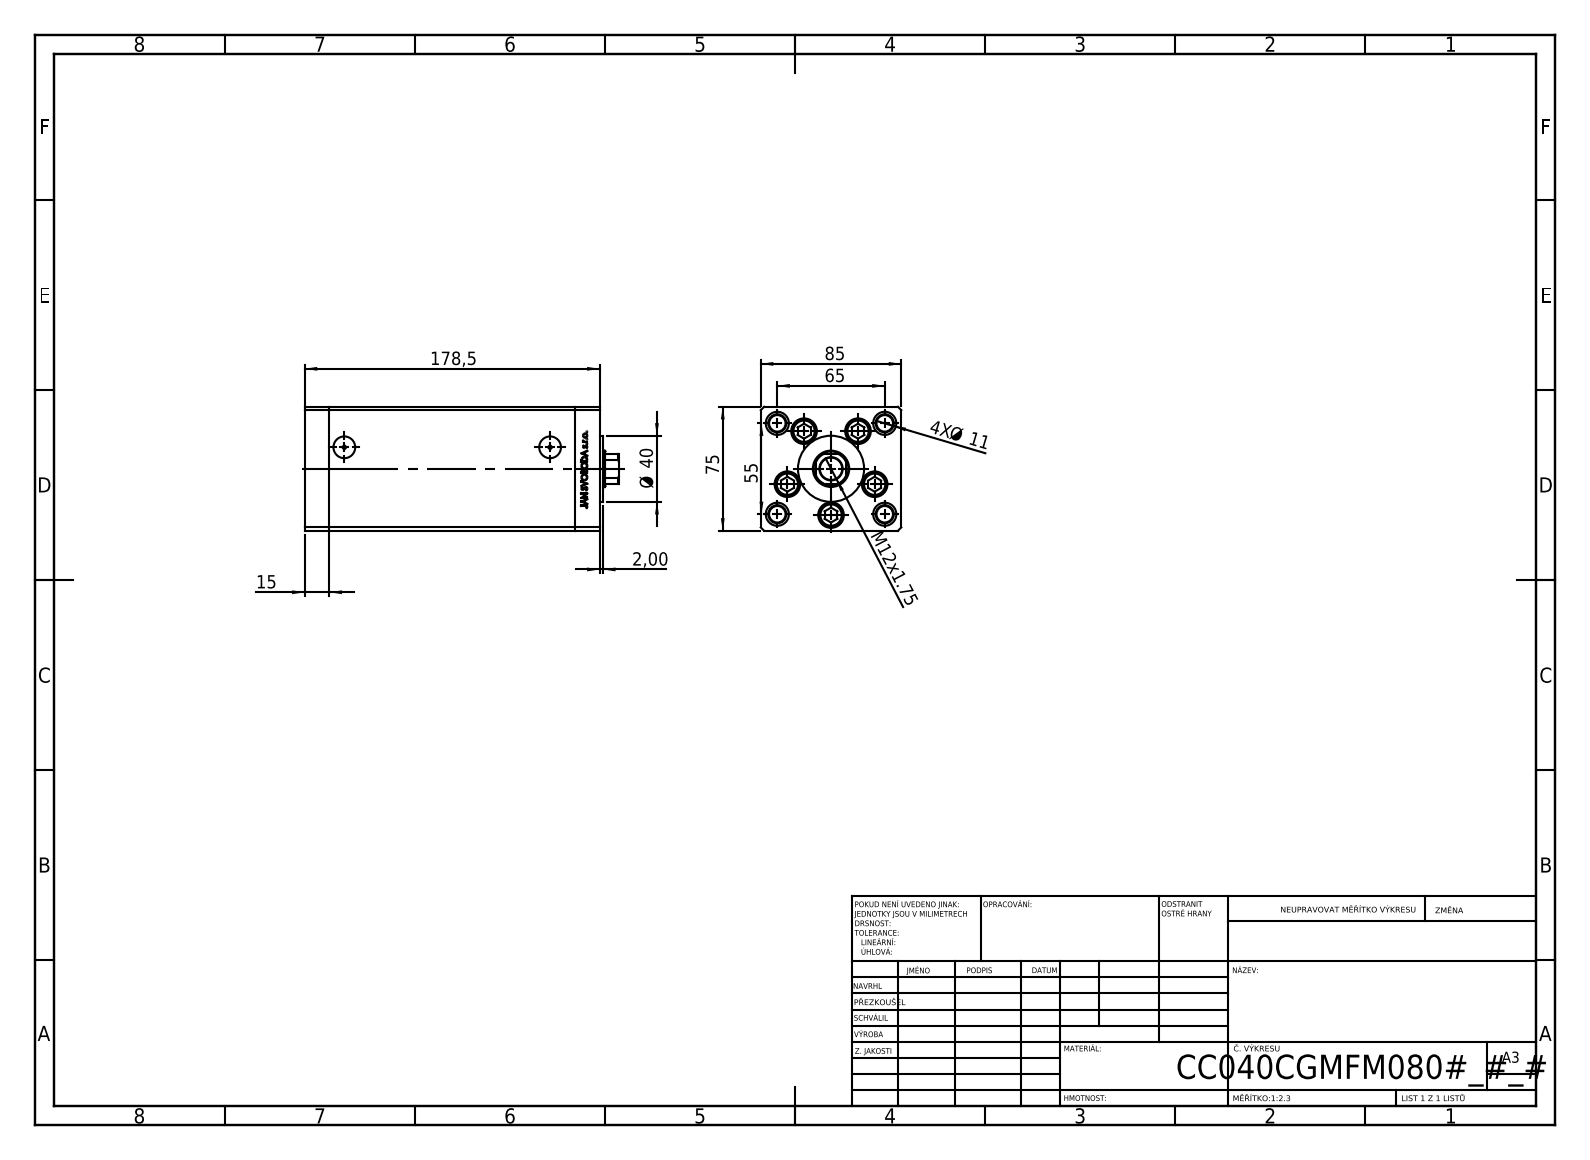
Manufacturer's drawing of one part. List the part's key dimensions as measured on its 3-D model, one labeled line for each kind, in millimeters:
Part name (STEP PRODUCT): V220C BACK_C; V220C FRONT; V220C_C MIDDLE; V220C_VC_C (+1 more)
STEP written by: SolidWorks 2019 (CONFIG_CONTROL_DESIGN)
Units: millimetres
Bodies: 13 solids, 1171 faces (542 planar, 167 cylindrical, 462 other)
Overall size (bounding box): 190 × 85 × 75
Volume: 945 382 mm³ · Surface area: 180 492 mm²
Round holes (diameter × count): ⌀11 ×9, ⌀15.5 ×5, ⌀10 ×4, ⌀14 ×4, ⌀2 ×2, ⌀13.16 ×2, ⌀13.5 ×1, ⌀14.5 ×1, ⌀22 ×1
Round bosses / shafts (diameter × count): ⌀8 ×5, ⌀14.5 ×4, ⌀40 ×1
Partial cylindrical surfaces — rounded edges, fillets, slot ends (radius × count): R0.93 ×2, R10.5 ×1
Main face-to-face distances: 85, 75, 15, 148.5, 163.5, 10.5, 178.5, 34.25, 144.25, 129.25
Hole centre spacings: 28, 42.57, 16.86, 19.17, 32.33, 32.5, 33.63, 37.33
